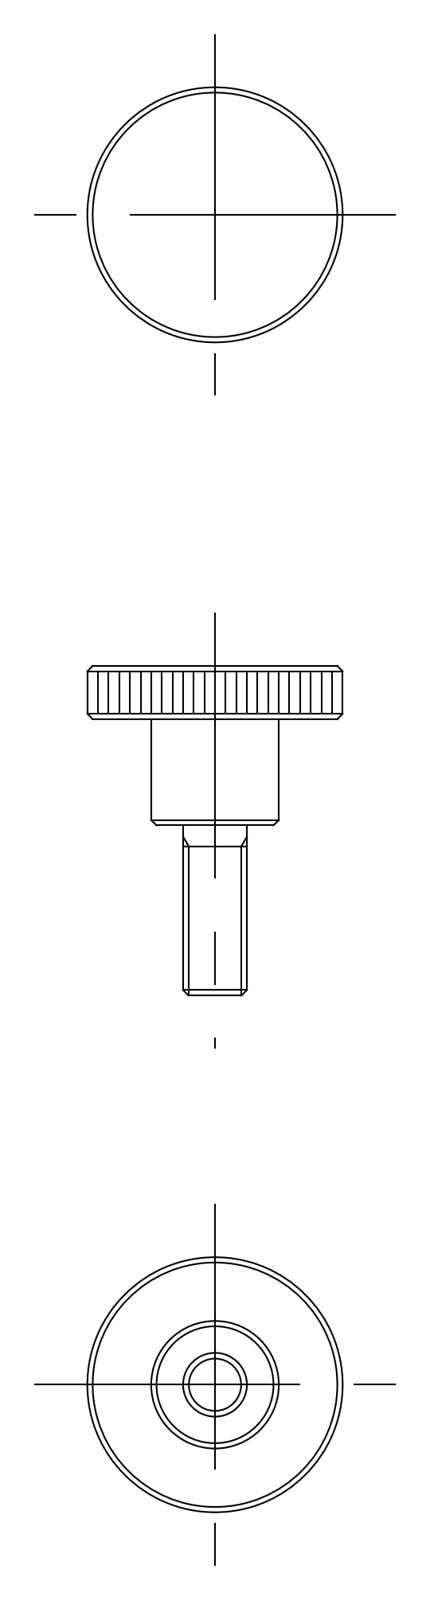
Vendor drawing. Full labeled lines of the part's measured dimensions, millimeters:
Part name (STEP PRODUCT): knob
STEP written by: CADfix (AUTOMOTIVE_DESIGN)
Units: millimetres
Bodies: 1 solid, 18 faces (0 planar, 0 cylindrical, 18 other)
Overall size (bounding box): 31 × 24 × 24
Volume: 3 827 mm³ · Surface area: 1 899 mm²
